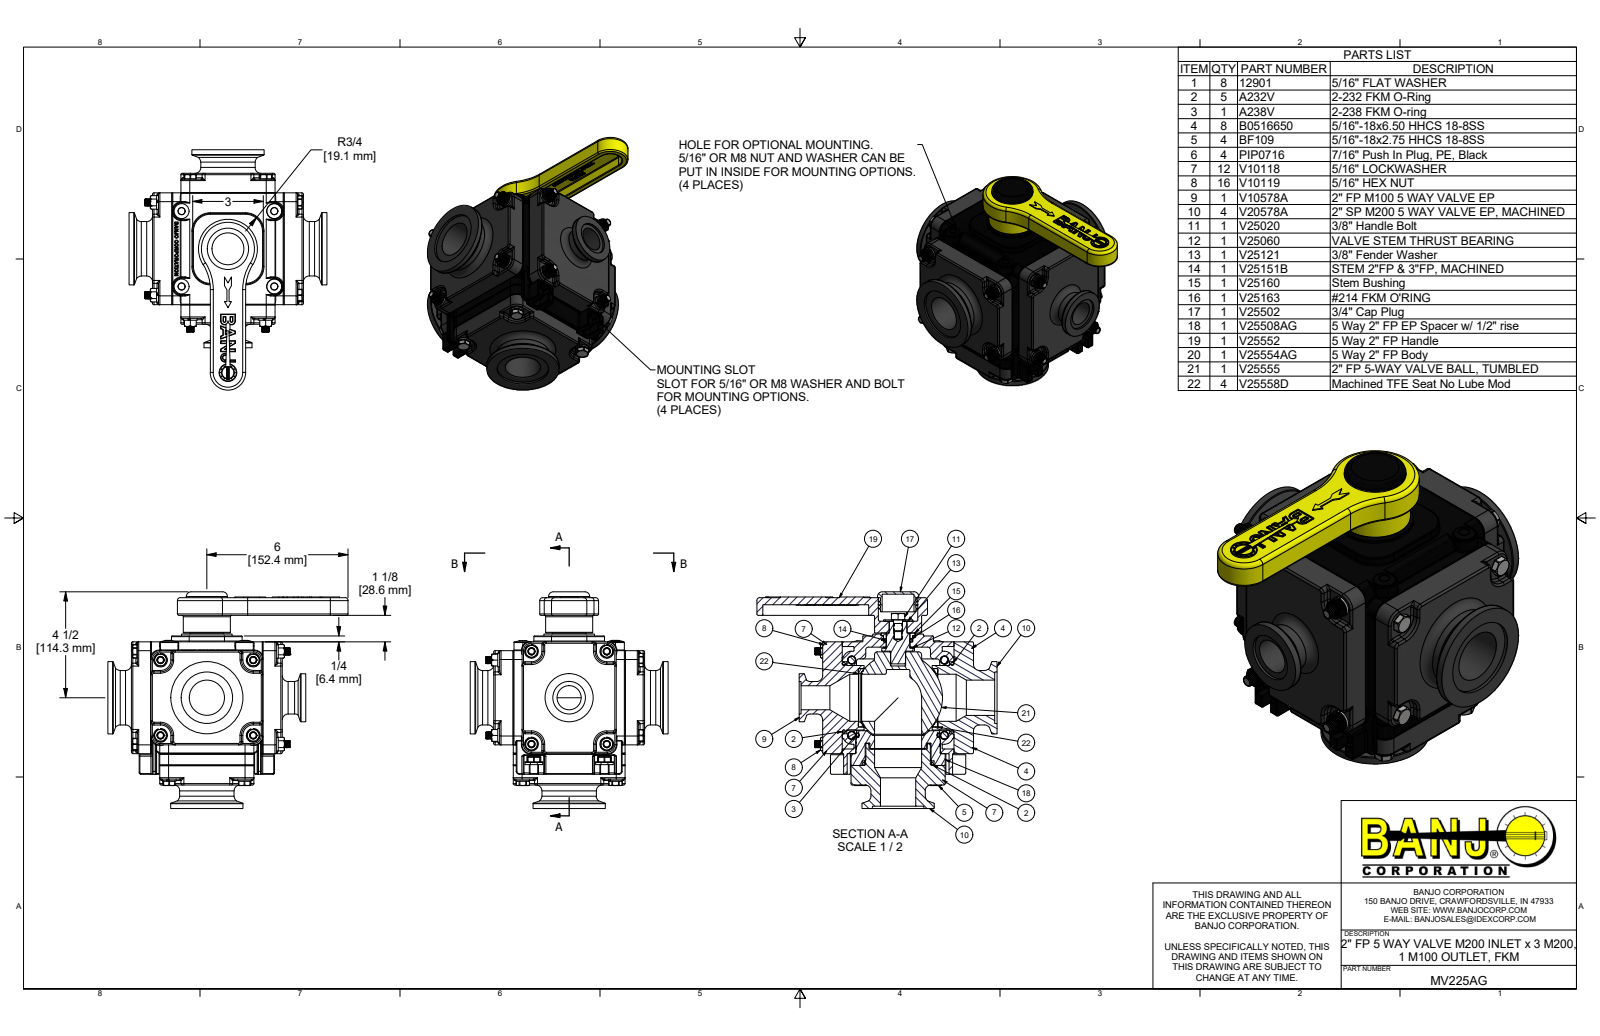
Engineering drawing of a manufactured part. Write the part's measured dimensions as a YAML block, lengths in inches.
part_name: "MV225AG; V25554AG; V25555; V25555M (+8 more)"
step_written_by: "Autodesk Inventor 2019 (AUTOMOTIVE_DESIGN)"
units: inches
bodies: {solids: 78, faces: 10858, planar: 3120, cylindrical: 3492, other: 4246}
overall_size: [10.205, 9.205, 8.41]
volume: 159.7
surface_area: 1164
round_holes:
  - {diameter: 0.252, count: 12}
  - {diameter: 0.313, count: 12}
  - {diameter: 0.322, count: 12}
  - {diameter: 0.33, count: 12}
  - {diameter: 0.35, count: 12}
  - {diameter: 0.3, count: 4}
  - {diameter: 0.344, count: 4}
  - {diameter: 2, count: 3}
  - {diameter: 2.19, count: 3}
  - {diameter: 2.48, count: 3}
  - {diameter: 2.8, count: 3}
  - {diameter: 3.06, count: 3}
round_bosses_or_shafts:
  - {diameter: 0.583, count: 12}
  - {diameter: 0.48, count: 12}
  - {diameter: 0.305, count: 12}
  - {diameter: 0.245, count: 12}
  - {diameter: 0.75, count: 4}
  - {diameter: 0.688, count: 4}
  - {diameter: 0.64, count: 4}
  - {diameter: 0.36, count: 4}
partial_cylinders:
  - {radius: 0.03, count: 678}
  - {radius: 0.06, count: 566}
  - {radius: 0.02, count: 66}
  - {radius: 0.125, count: 53}
  - {radius: 0.375, count: 29}
  - {radius: 0.5, count: 13}
  - {radius: 0.415, count: 12}
  - {radius: 0.665, count: 12}
face_to_face_distances: [0.83, 0.25, 0.83, 0.375, 4.375, 5.58, 4.75, 5.58, 1.205, 4.75]
hole_center_spacings: [2.538, 3.2, 3.94, 5.076, 4.156, 7.137, 5.26]
